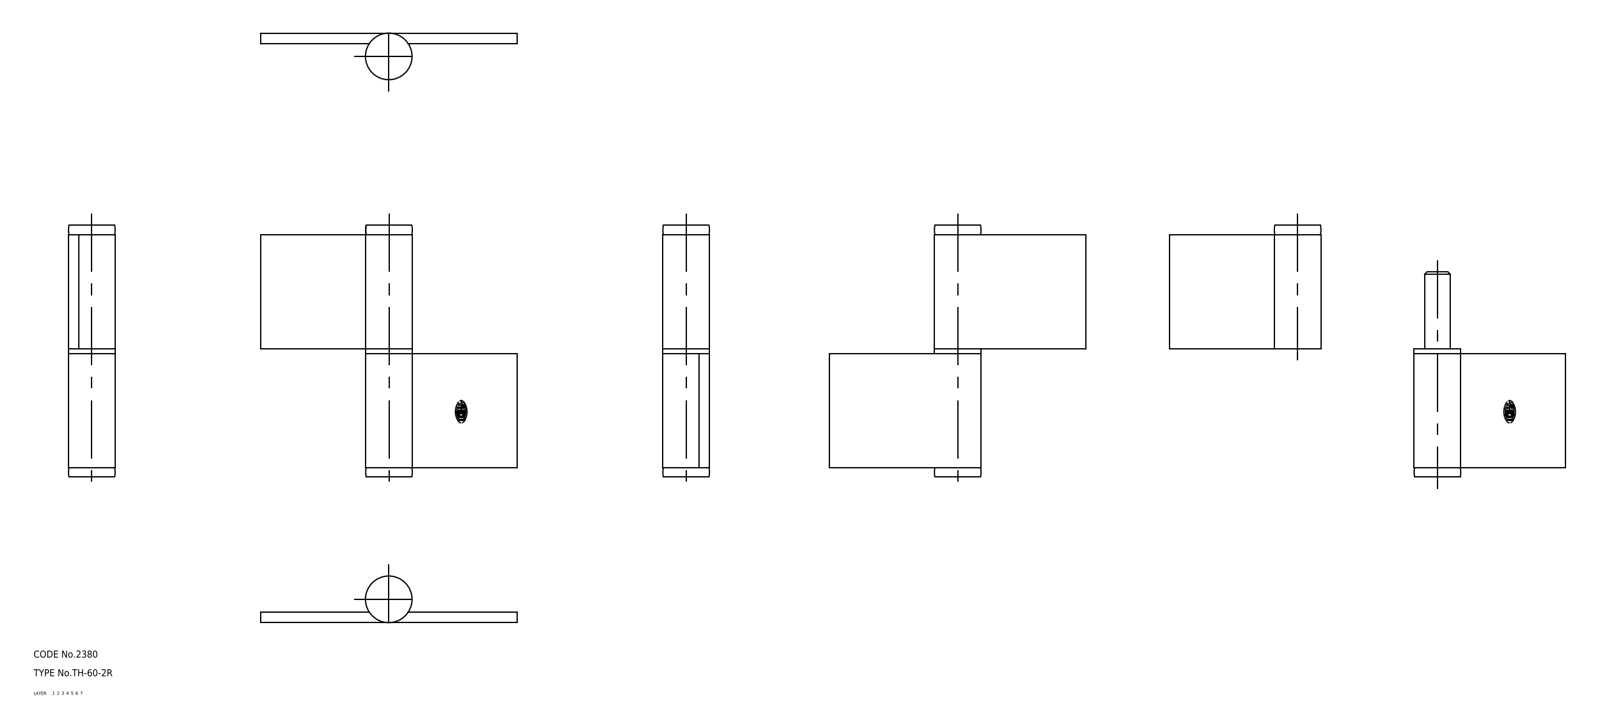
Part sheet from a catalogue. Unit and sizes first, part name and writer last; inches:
Units: inches
Overall size (bounding box): 4.331 × 4.252 × 0.787
Volume: 3.307 in³ · Surface area: 41.87 in²
Bodies: 5 solids, 34 faces (0 planar, 0 cylindrical, 34 other)
Part name (STEP PRODUCT): hinge piece; washer; shaft; rivet (+1 more)
STEP written by: CADfix (AUTOMOTIVE_DESIGN)
